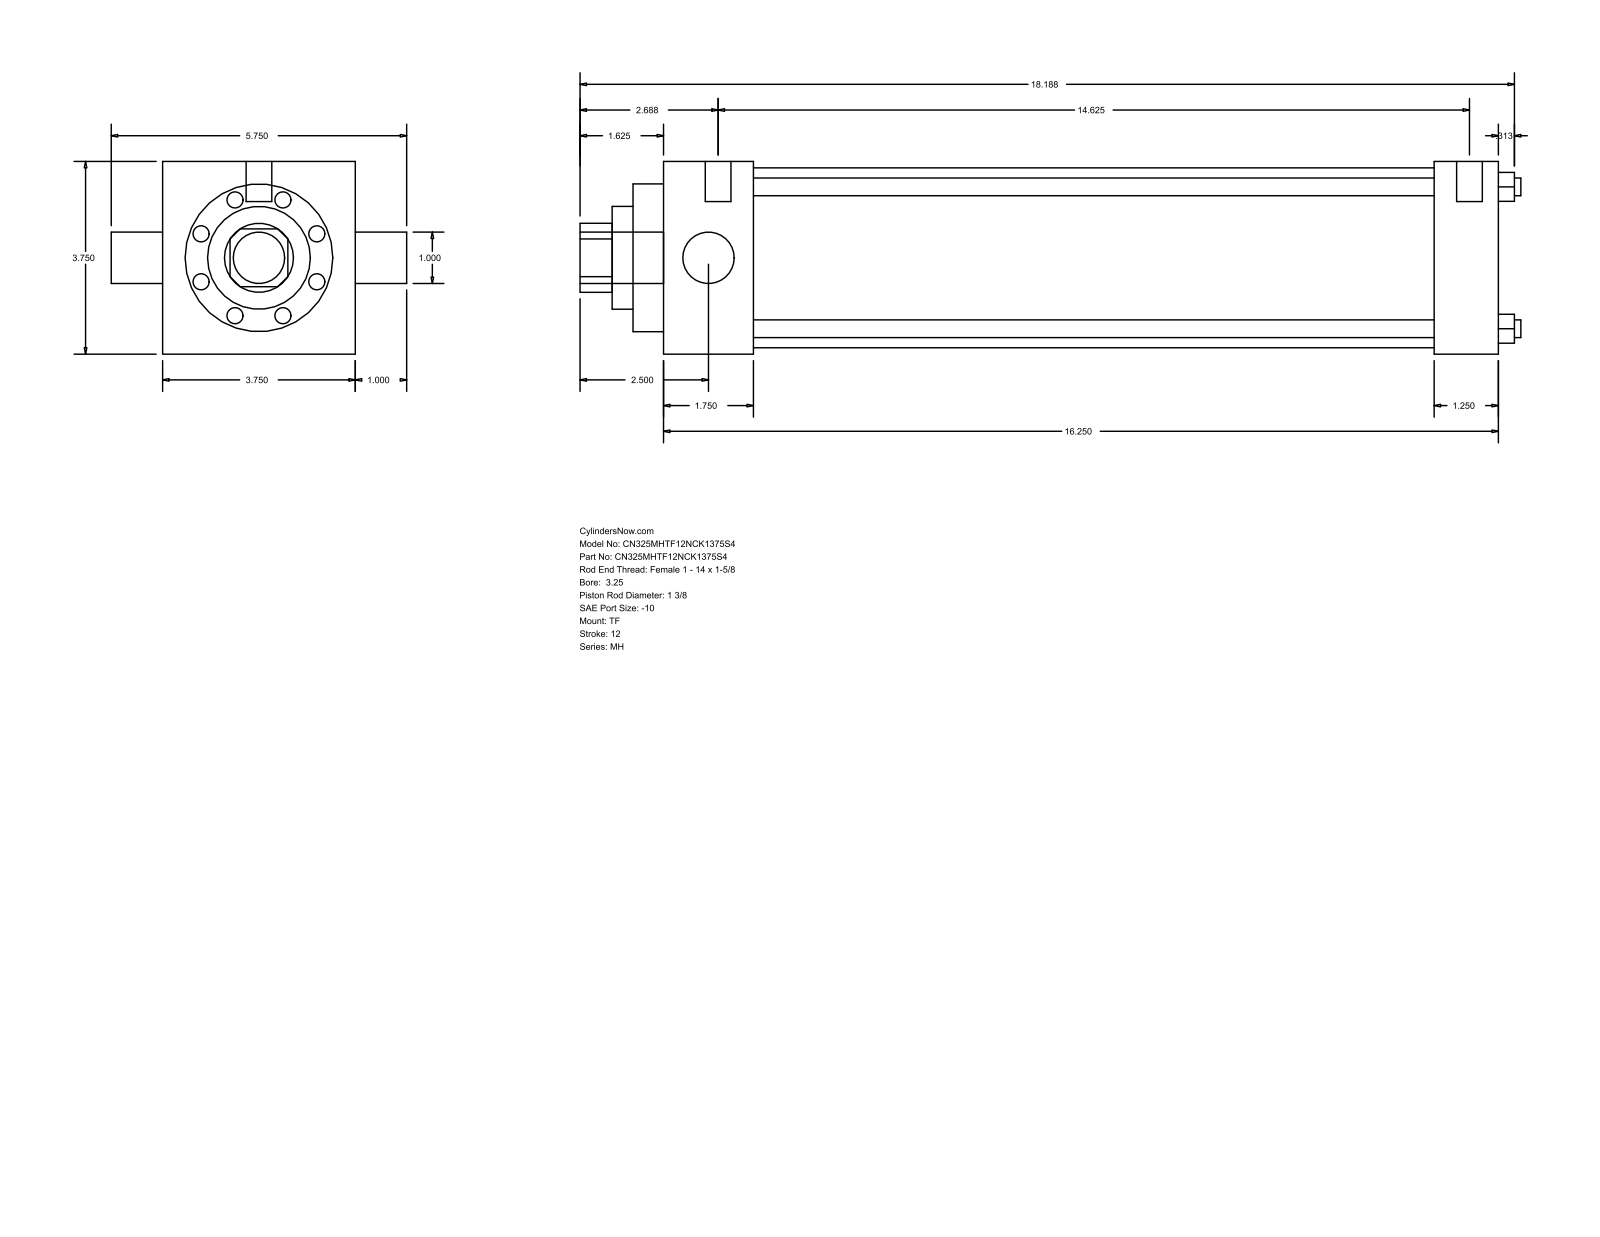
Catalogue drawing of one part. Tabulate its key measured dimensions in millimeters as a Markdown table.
| quantity | value |
| --- | --- |
| part name | MH_TF__0325_1.375 |
| STEP written by | GSSL Pune (CONFIG_CONTROL_DESIGN) |
| units | millimeters |
| bodies | 0 solids, 86 faces (61 planar, 25 cylindrical, 0 other) |
| overall size | 465.14 × 146.05 × 95.25 |
| round holes (diameter × count) | 8.76 × 4, 25.4 × 1, 34.92 × 1, 50.8 × 1, 73.03 × 1, 88.9 × 1 |
| round bosses / shafts (diameter × count) | 5.56 × 3, 12.7 × 2, 25.4 × 1 |
| partial cylindrical surfaces (radius × count) | 17.06 × 1 |
| main face-to-face distances | 95.24, 412.75, 44.45, 381, 336.55, 368.3, 31.75, 15.08, 59.53, 396.08 |
| hole center spacings | 49.57, 70.1, 99.14 |
